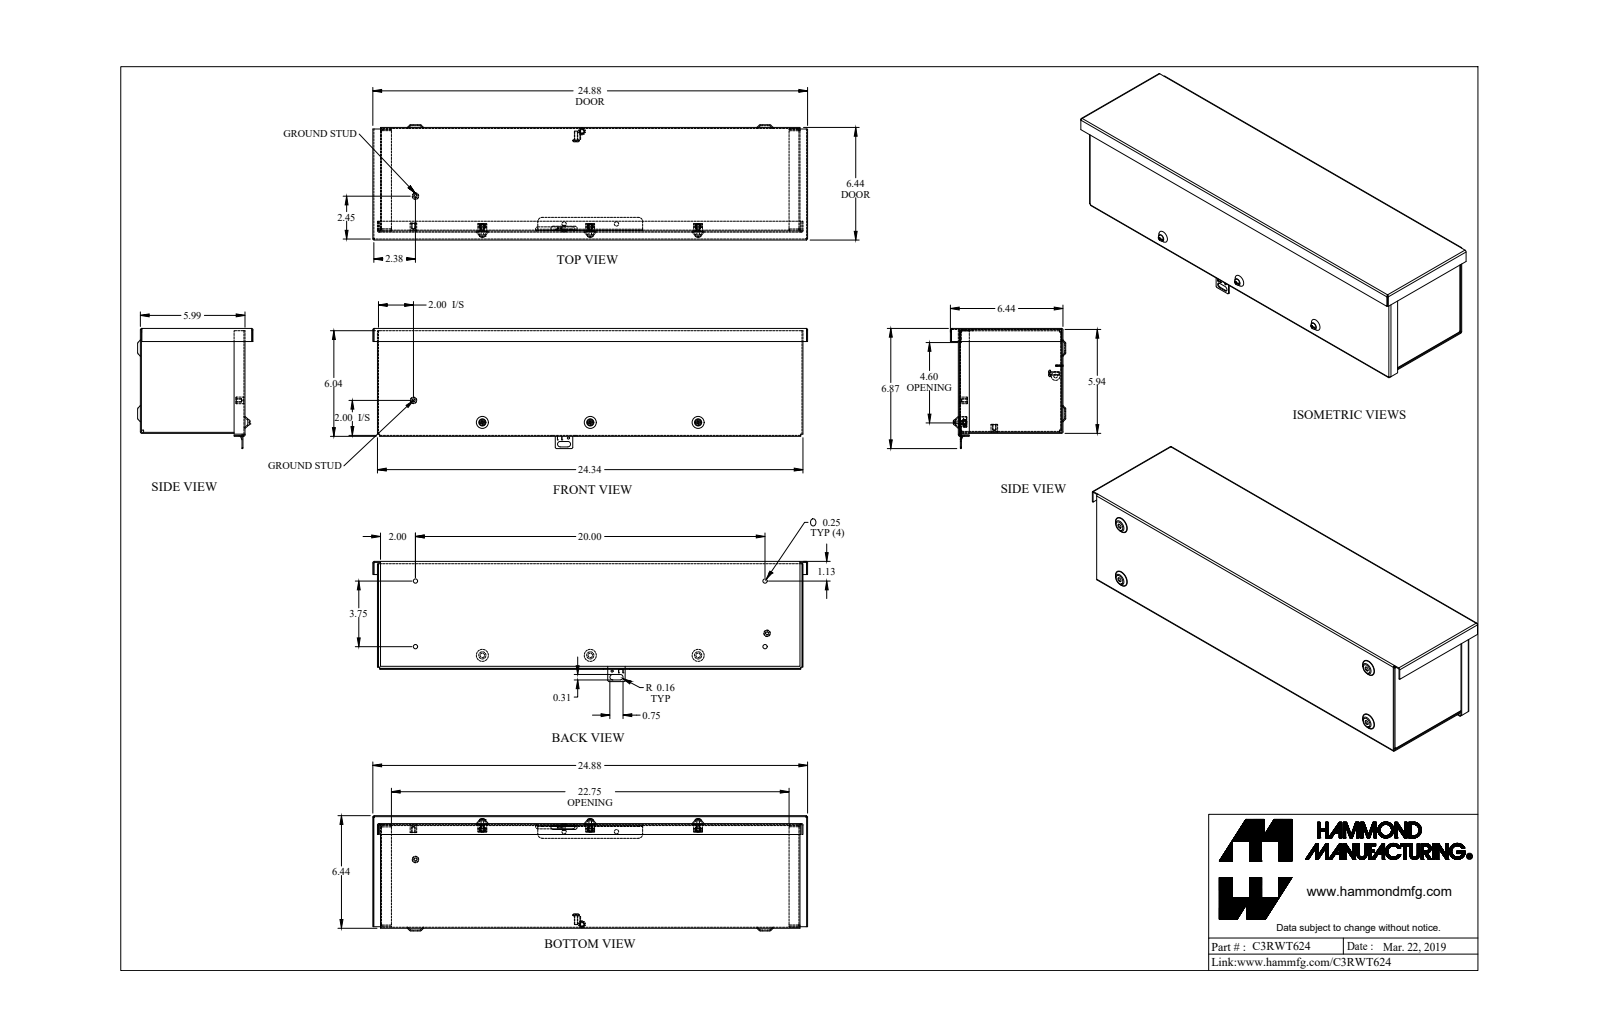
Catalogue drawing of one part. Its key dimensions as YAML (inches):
part_name: "C3RWT624_Default"
step_written_by: "SolidWorks 2019 (CONFIG_CONTROL_DESIGN)"
units: inches
bodies: {solids: 22, faces: 766, planar: 415, cylindrical: 239, other: 112}
overall_size: [24.875, 6.871, 6.594]
volume: 43.64
surface_area: 1542
round_holes:
  - {diameter: 0.25, count: 6}
  - {diameter: 0.156, count: 5}
  - {diameter: 0.214, count: 3}
  - {diameter: 0.23, count: 3}
  - {diameter: 0.203, count: 2}
  - {diameter: 0.125, count: 1}
  - {diameter: 0.137, count: 1}
  - {diameter: 0.2, count: 1}
  - {diameter: 0.215, count: 1}
round_bosses_or_shafts:
  - {diameter: 0.19, count: 4}
  - {diameter: 0.148, count: 3}
  - {diameter: 0.375, count: 2}
  - {diameter: 0.5, count: 1}
  - {diameter: 0.367, count: 1}
  - {diameter: 0.21, count: 1}
  - {diameter: 0.152, count: 1}
  - {diameter: 0.125, count: 1}
partial_cylinders:
  - {radius: 0.029, count: 18}
  - {radius: 0.086, count: 18}
  - {radius: 0.125, count: 13}
  - {radius: 0.08, count: 12}
  - {radius: 0.108, count: 12}
  - {radius: 0.022, count: 6}
  - {radius: 0.25, count: 6}
  - {radius: 0.016, count: 4}
face_to_face_distances: [0.057, 5.943, 5.928, 5.871, 5.886, 6, 5.985, 23.943, 0.172, 24]
hole_center_spacings: [3.943, 16.637, 2.402, 3.75, 3.861, 5.719, 6.172, 6.95]
